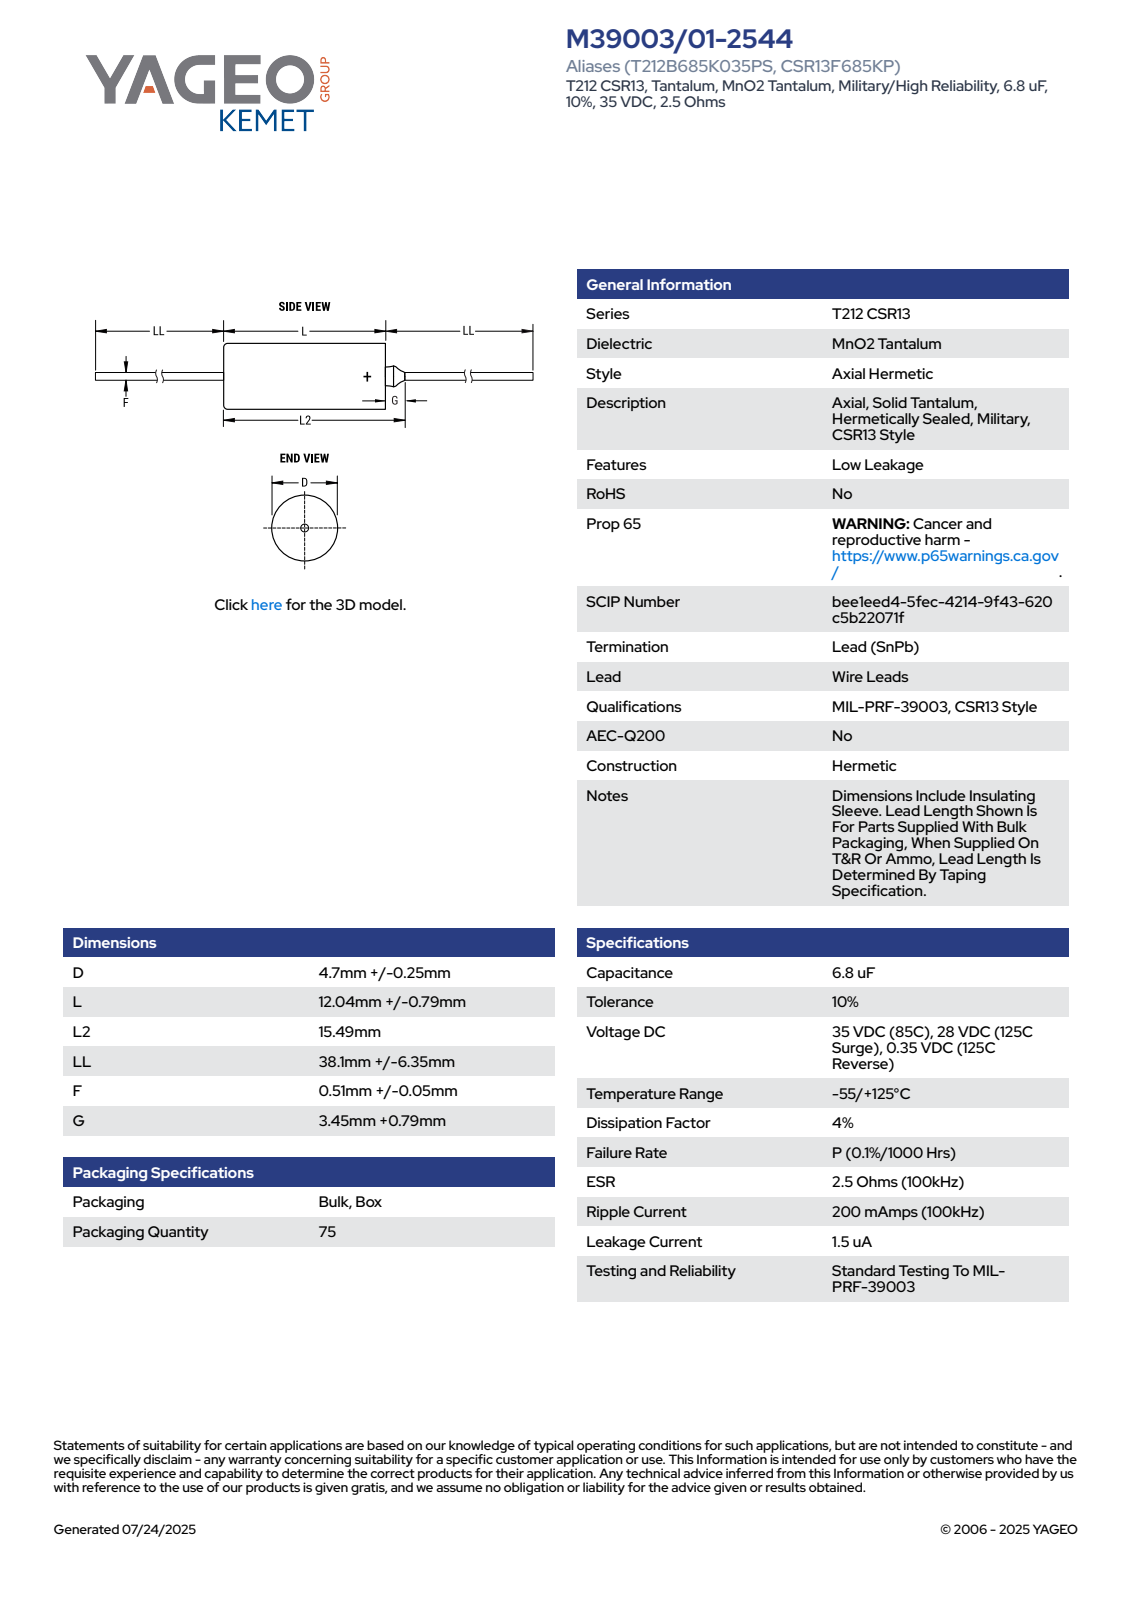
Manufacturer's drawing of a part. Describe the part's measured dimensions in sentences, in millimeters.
The part is named "CTAM_AHTWG_D4.95L12.83L215.49LL44.45F0.56G4.24". Its 3-D file was written by "SolidWorks 2014 (AUTOMOTIVE_DESIGN)". It is 1 solid with 99 faces: 30 planar, 30 cylindrical and 39 other. Overall it measures 101.73 by 4.95 by 4.95 millimeters. Its volume is 221 cubic millimeters and its surface area 454 square millimeters. Round holes: 1 of diameter 4.55. Round bosses or shafts: 1 of diameter 4.95, 1 of diameter 1.33, 1 of diameter 1.3, 1 of diameter 0.56. Partial cylindrical surfaces (rounded edges, fillets, slot ends): 1 of radius 2.46. The main face-to-face distances are 9.48, 12.66, 3.18, 44.45, 57.28, 44.62, 54.1, 101.73, 57.11, 47.63.
